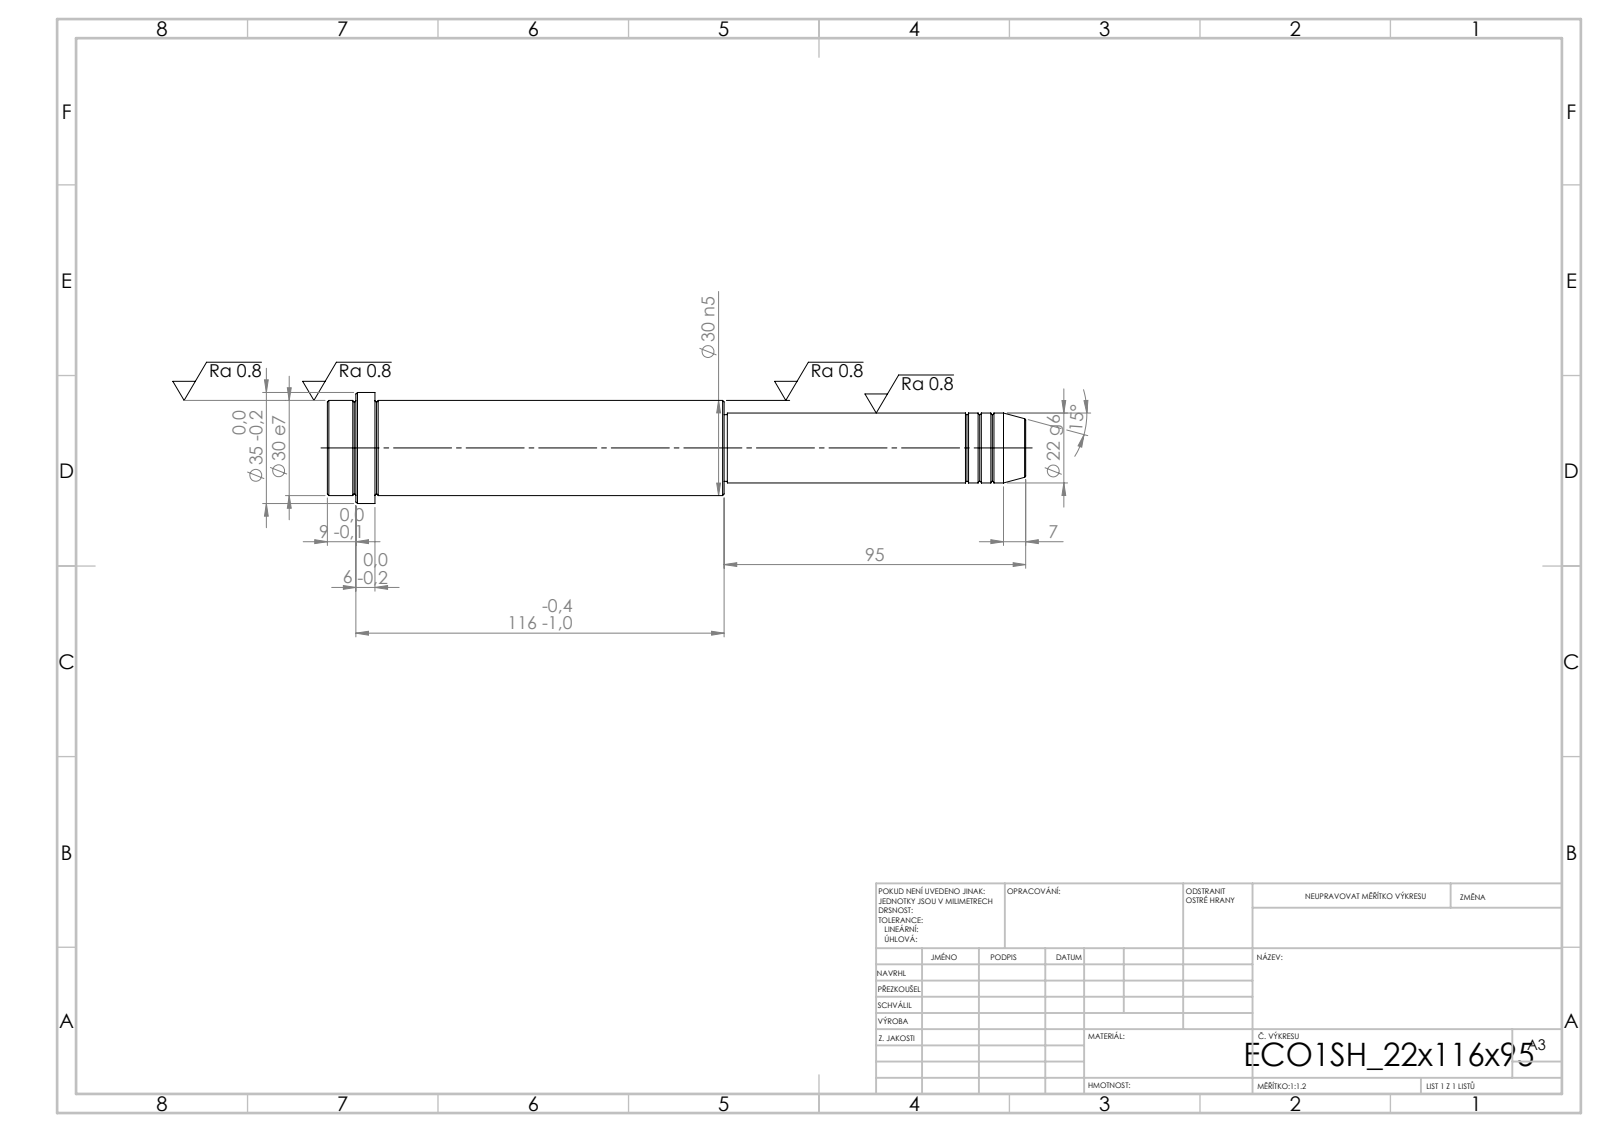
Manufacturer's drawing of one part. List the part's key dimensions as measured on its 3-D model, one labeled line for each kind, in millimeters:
STEP written by: SolidWorks 2019 (CONFIG_CONTROL_DESIGN)
Units: millimetres
Bodies: 1 solid, 52 faces (6 planar, 16 cylindrical, 30 other)
Overall size (bounding box): 220 × 35 × 35
Volume: 125 348 mm³ · Surface area: 20 401 mm²
Round bosses / shafts (diameter × count): ⌀35 ×1, ⌀30 ×1, ⌀22 ×1, ⌀21 ×1
Main face-to-face distances: 125, 110, 15, 95, 205, 220, 211, 116, 6, 9
